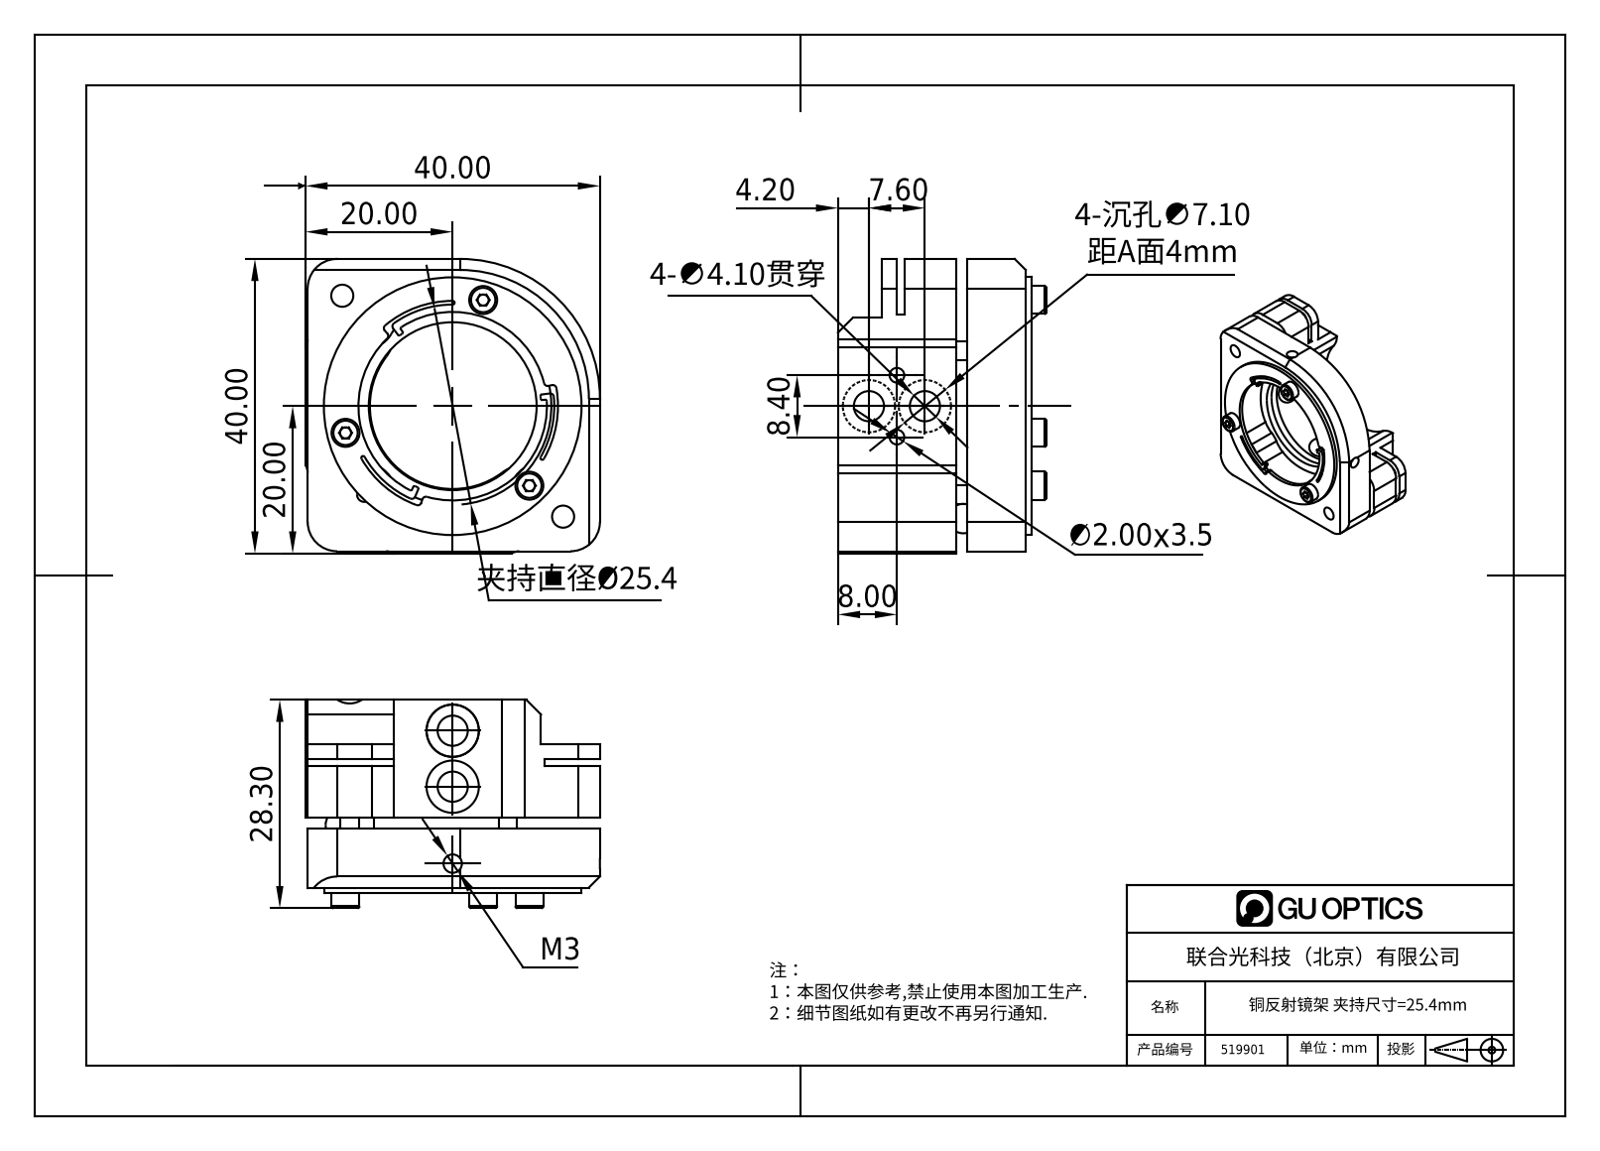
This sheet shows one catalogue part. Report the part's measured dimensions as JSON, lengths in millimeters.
{"part_name": "519901", "step_written_by": "SolidWorks 2020 (CONFIG_CONTROL_DESIGN)", "units": "millimeters", "bodies": {"solids": 10, "faces": 272, "planar": 139, "cylindrical": 120, "other": 13}, "overall_size": [40, 40, 28.3], "volume_mm3": 15584, "surface_area_mm2": 11957, "round_holes": [[2, 10], [2.5, 4], [4.1, 4], [7.1, 4], [3.5, 3], [6, 3], [3, 2], [4.5, 2], [5, 2], [22.8, 1], [25.6, 1]], "round_bosses_or_shafts": [[4.5, 3], [3.8, 3], [2.5, 3], [35, 1]], "partial_cylinders_radius": [[0.2, 9], [0.5, 9], [5, 8], [4, 6], [2, 4], [0.25, 3], [3, 2], [11.24, 1]], "face_to_face_distances": [8, 9.5, 1.5, 17.5, 8.8, 0.8, 10.3, 16, 25.5, 26.3], "hole_center_spacings": [5.66, 14.86, 15, 4.77, 7.57, 7.6, 8.4, 10.45]}
